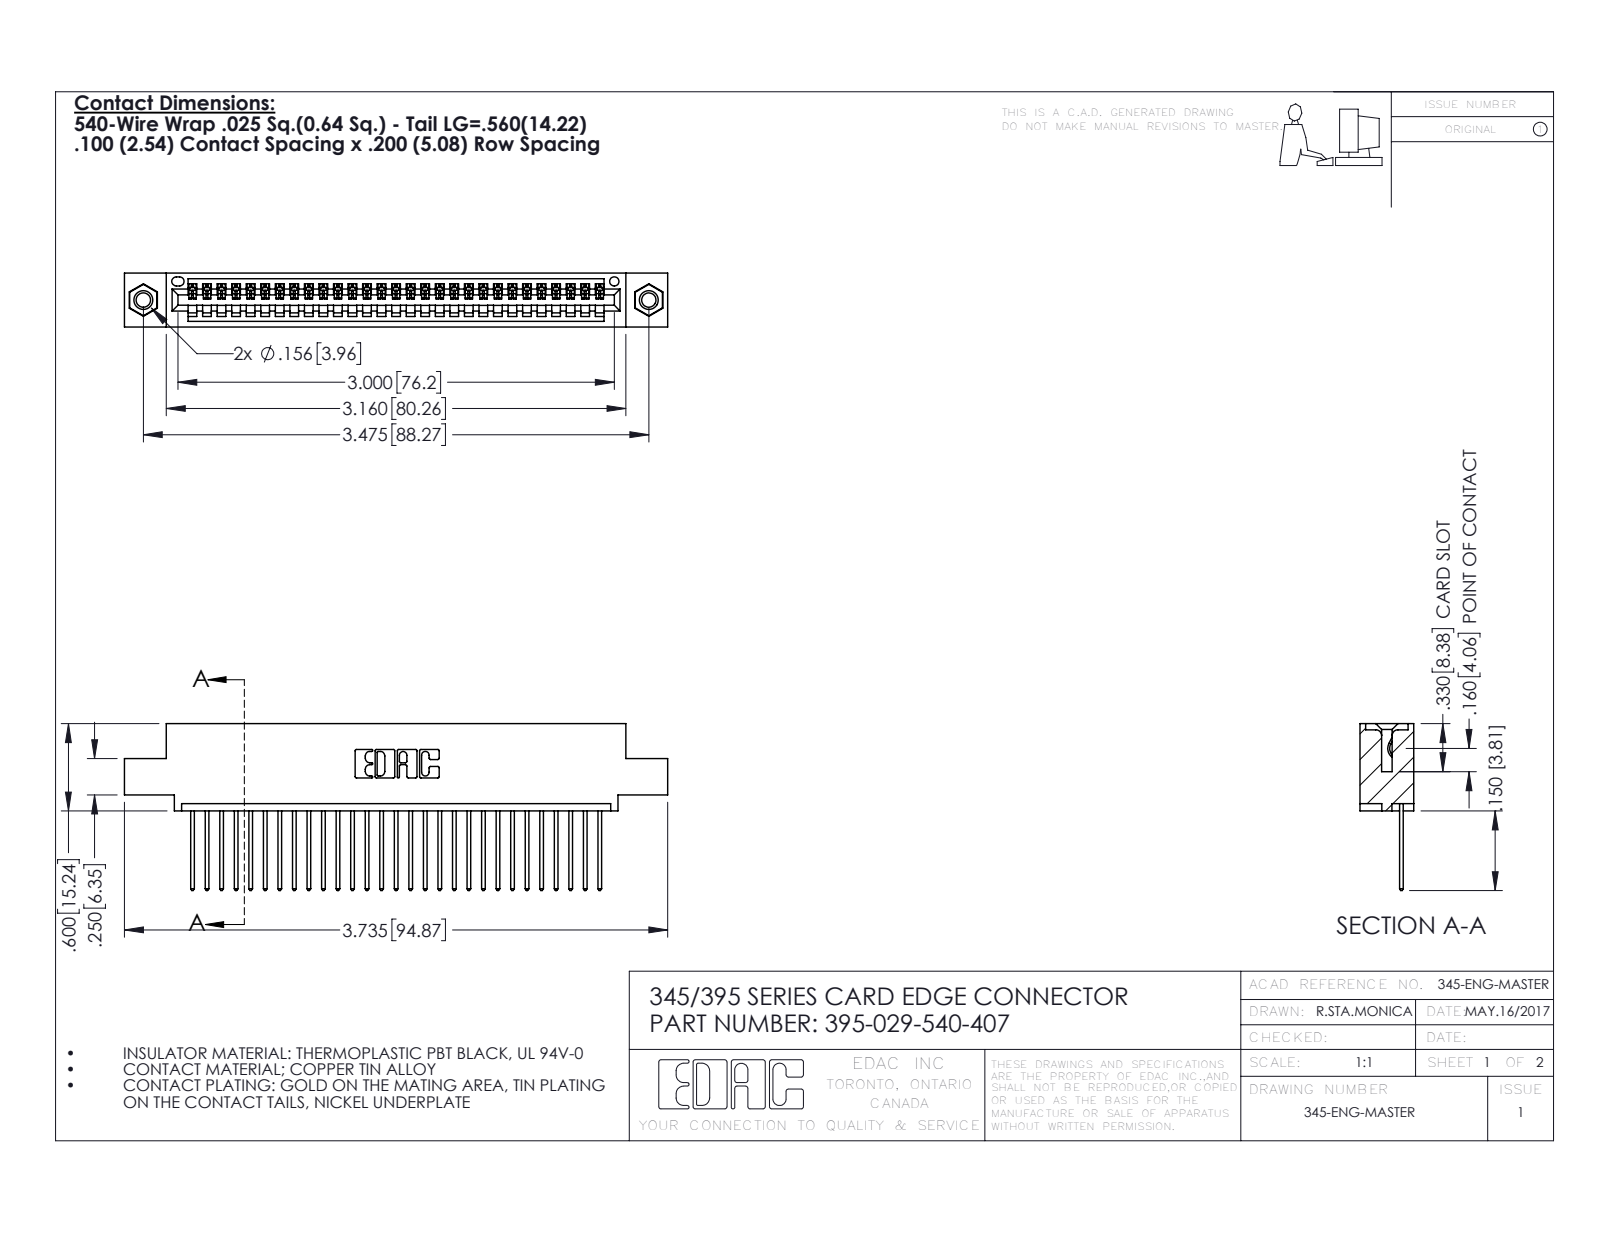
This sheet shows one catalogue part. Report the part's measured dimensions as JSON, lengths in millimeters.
{"part_name": "345 Part_0.110 Offset - 0.156 Dia-TI; 395-029-540-407; 345-250-001_345-250-005-103; 345-292-001_345-293-140", "step_written_by": "SolidWorks 2016 (CONFIG_CONTROL_DESIGN)", "units": "millimeters", "bodies": {"solids": 32, "faces": 1872, "planar": 1276, "cylindrical": 580, "other": 16}, "overall_size": [94.9, 29.1, 9.4], "volume_mm3": 8850, "surface_area_mm2": 11990, "round_holes": [[2.5, 2], [3.2, 2], [4, 2], [1.6, 1]], "round_bosses_or_shafts": [[3.9, 2]], "partial_cylinders_radius": [[0.2, 58], [0.3, 58], [0.3, 22], [0.2, 6], [0.8, 6], [0.7, 3], [0.8, 2], [1, 2]], "face_to_face_distances": [1.8, 7.6, 9.4, 5.1, 2.5, 6.9, 0.6, 5.7, 3.8, 1.8], "hole_center_spacings": [6.9, 82.3, 88.3]}
